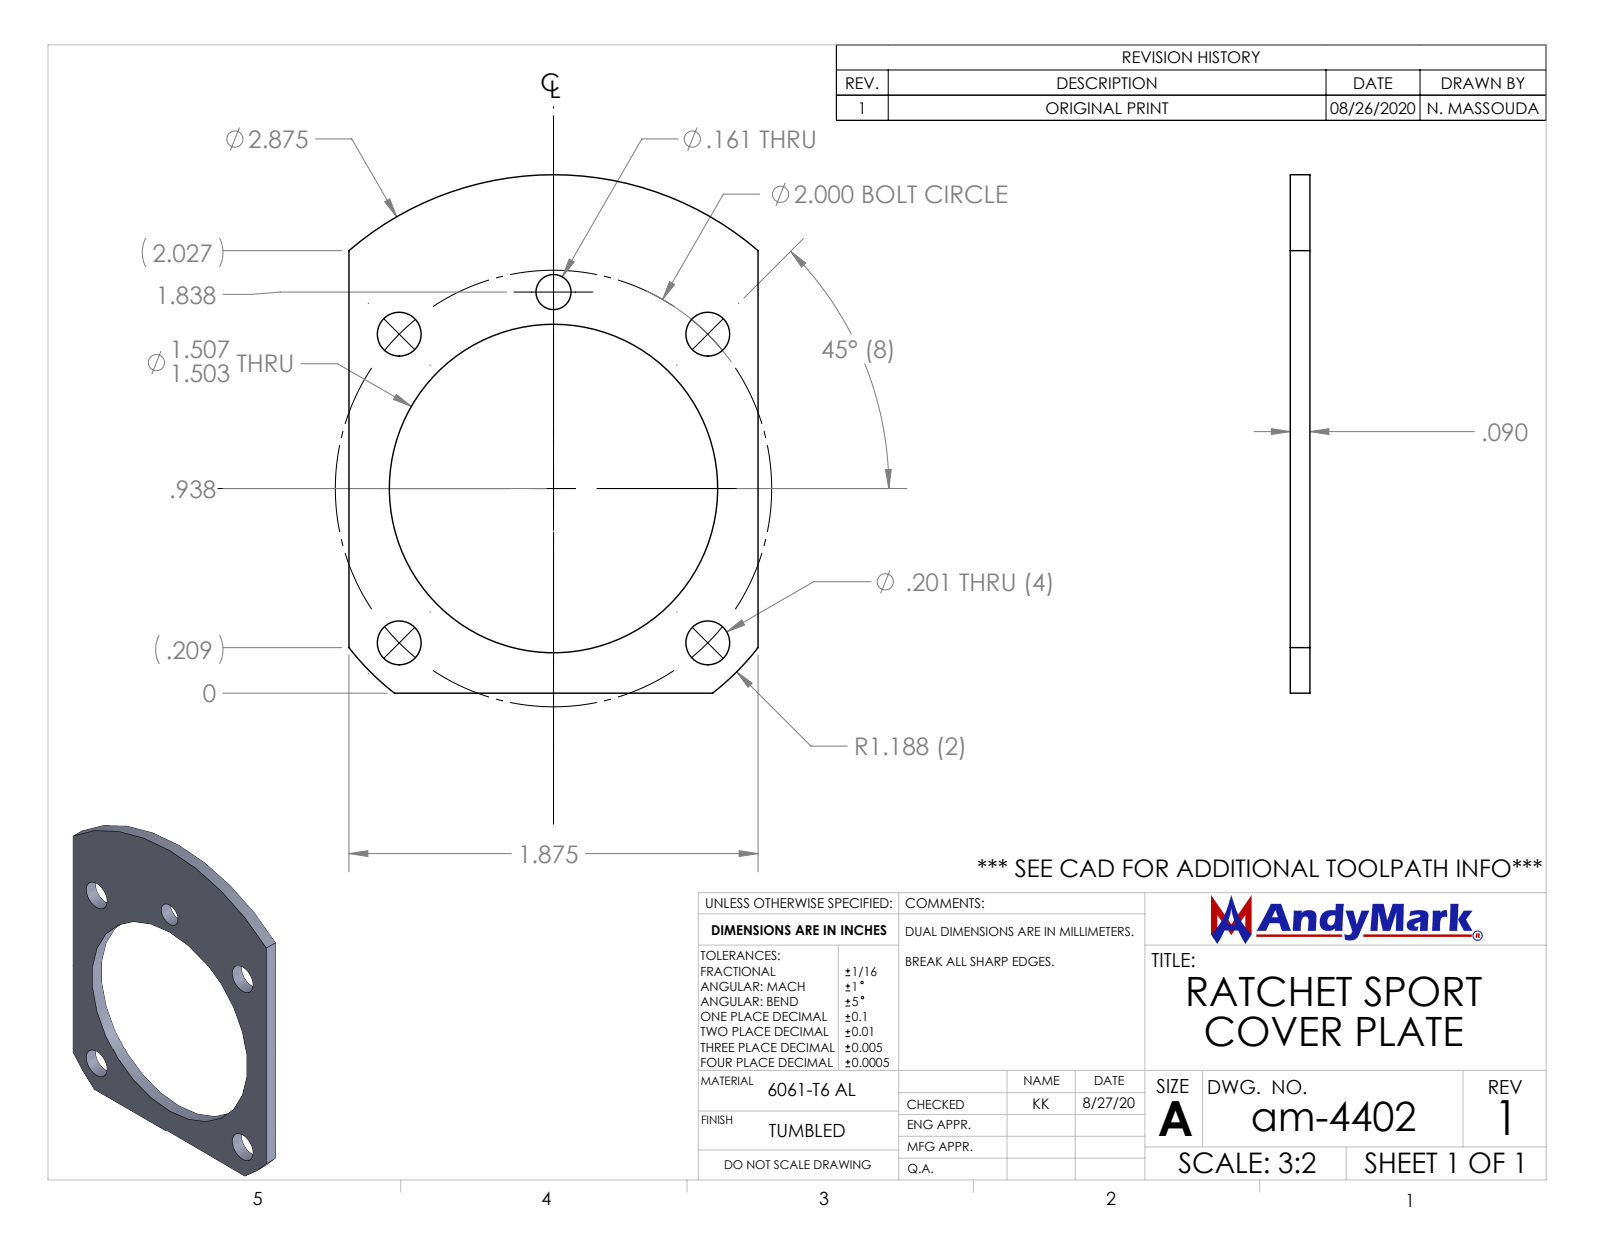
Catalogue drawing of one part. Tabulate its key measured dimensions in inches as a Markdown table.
| quantity | value |
| --- | --- |
| part name | am-4402 Ratchet Sport Cover Plate |
| STEP written by | SolidWorks 2019 (CONFIG_CONTROL_DESIGN) |
| units | inches |
| bodies | 1 solid, 21 faces (5 planar, 16 cylindrical, 0 other) |
| overall size | 2.375 × 1.875 × 0.09 |
| volume | 0.205 in³ |
| surface area | 5.957 in² |
| round holes (diameter × count) | 0.201 × 4, 0.161 × 1, 1.505 × 1 |
| partial cylindrical surfaces (radius × count) | 1.187 × 1, 1.437 × 1 |
| main face-to-face distances | 0.09, 1.875 |
| hole center spacings | 1, 1.414, 0.733, 1.756, 2, 0.9 |
